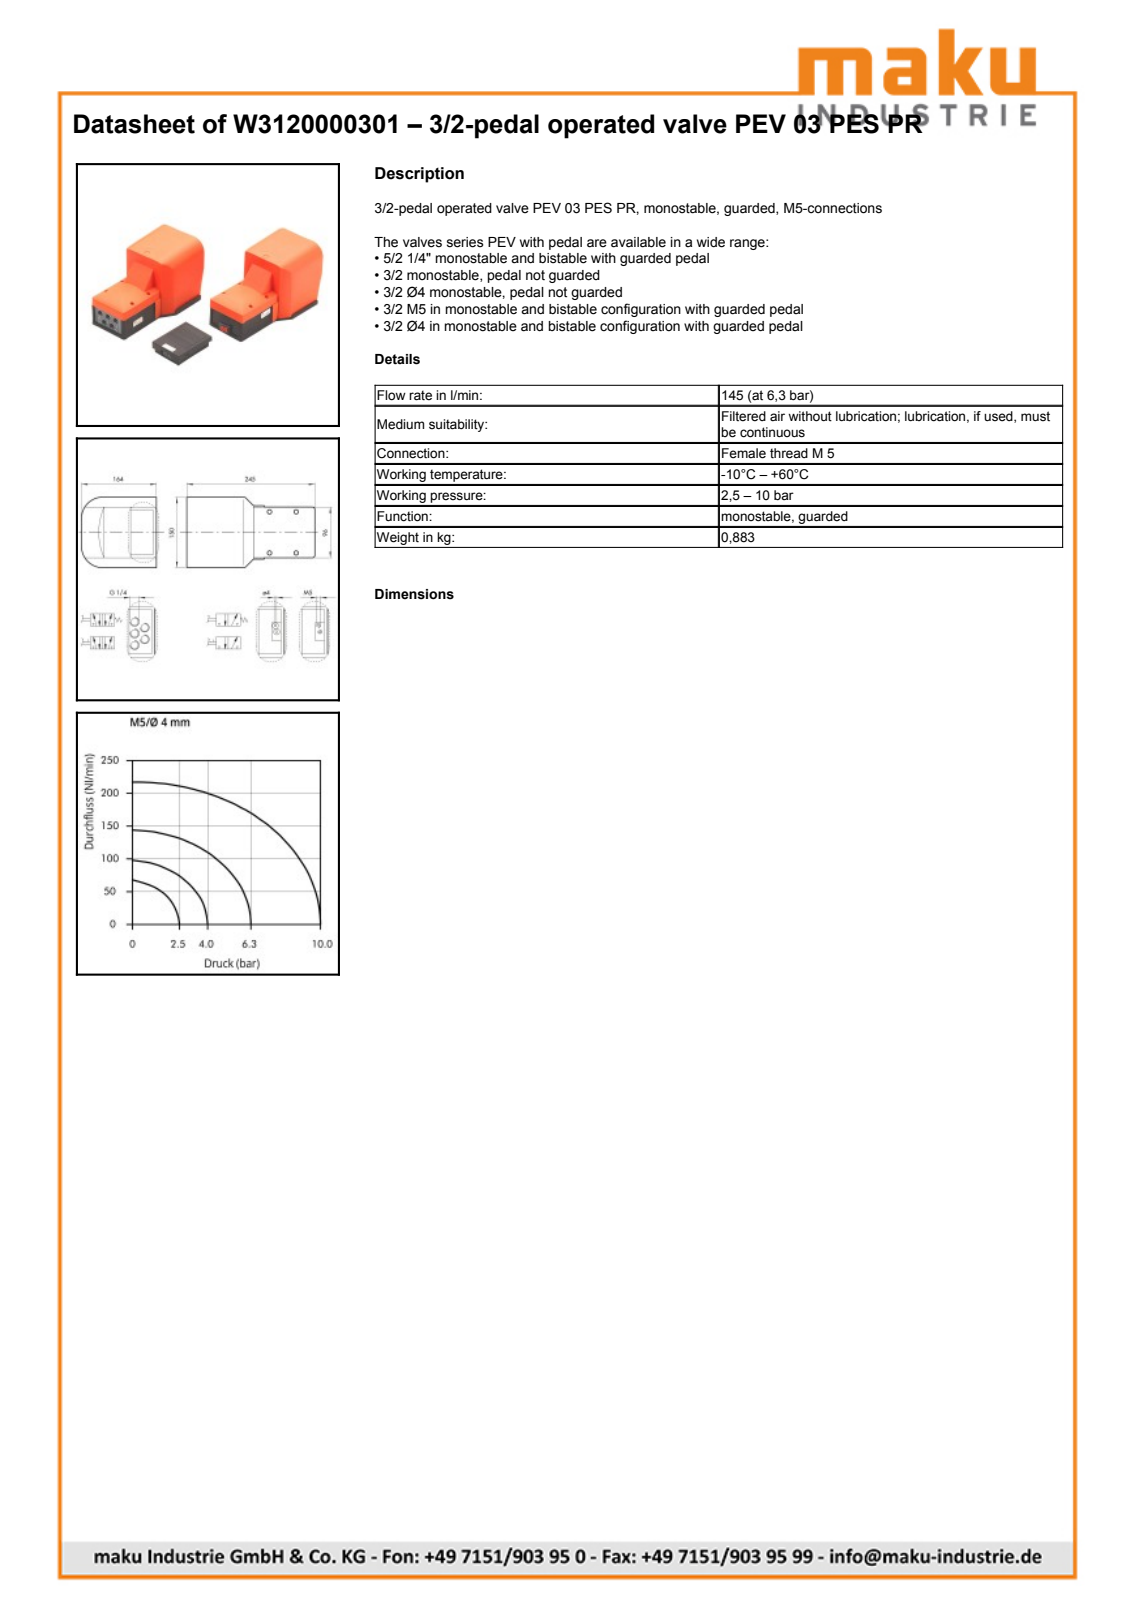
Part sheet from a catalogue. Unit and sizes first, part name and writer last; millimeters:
Units: millimetres
Overall size (bounding box): 242.5 × 164 × 150
Round holes (diameter × count): ⌀4 ×4, ⌀2.4 ×2, ⌀4.13 ×2, ⌀4.5 ×2, ⌀8 ×1, ⌀28 ×1
Round bosses / shafts (diameter × count): ⌀13 ×4, ⌀9 ×4, ⌀8 ×4, ⌀10 ×2, ⌀36 ×1, ⌀4.2 ×1
Partial cylindrical surfaces — rounded edges, fillets, slot ends (radius × count): R4 ×4, R6 ×3, R1.5 ×2, R22.5 ×2, R25 ×2
Main face-to-face distances: 2.5, 7, 142.5, 118, 24.5, 120.5, 22, 27, 145, 115.5
Hole centre spacings: 9.34, 51, 80, 82.58, 94.87, 129.58, 4.75, 10.41
Volume: 556 795 mm³ · Surface area: 304 778 mm²
Bodies: 8 solids, 425 faces (338 planar, 62 cylindrical, 25 other)
Part name (STEP PRODUCT): W3120000301(0SPR); W3120000301Pedal; W3120000301Body; W3120000301Body1 (+2 more)
STEP written by: PARTsolutions (AUTOMOTIVE_DESIGN)
